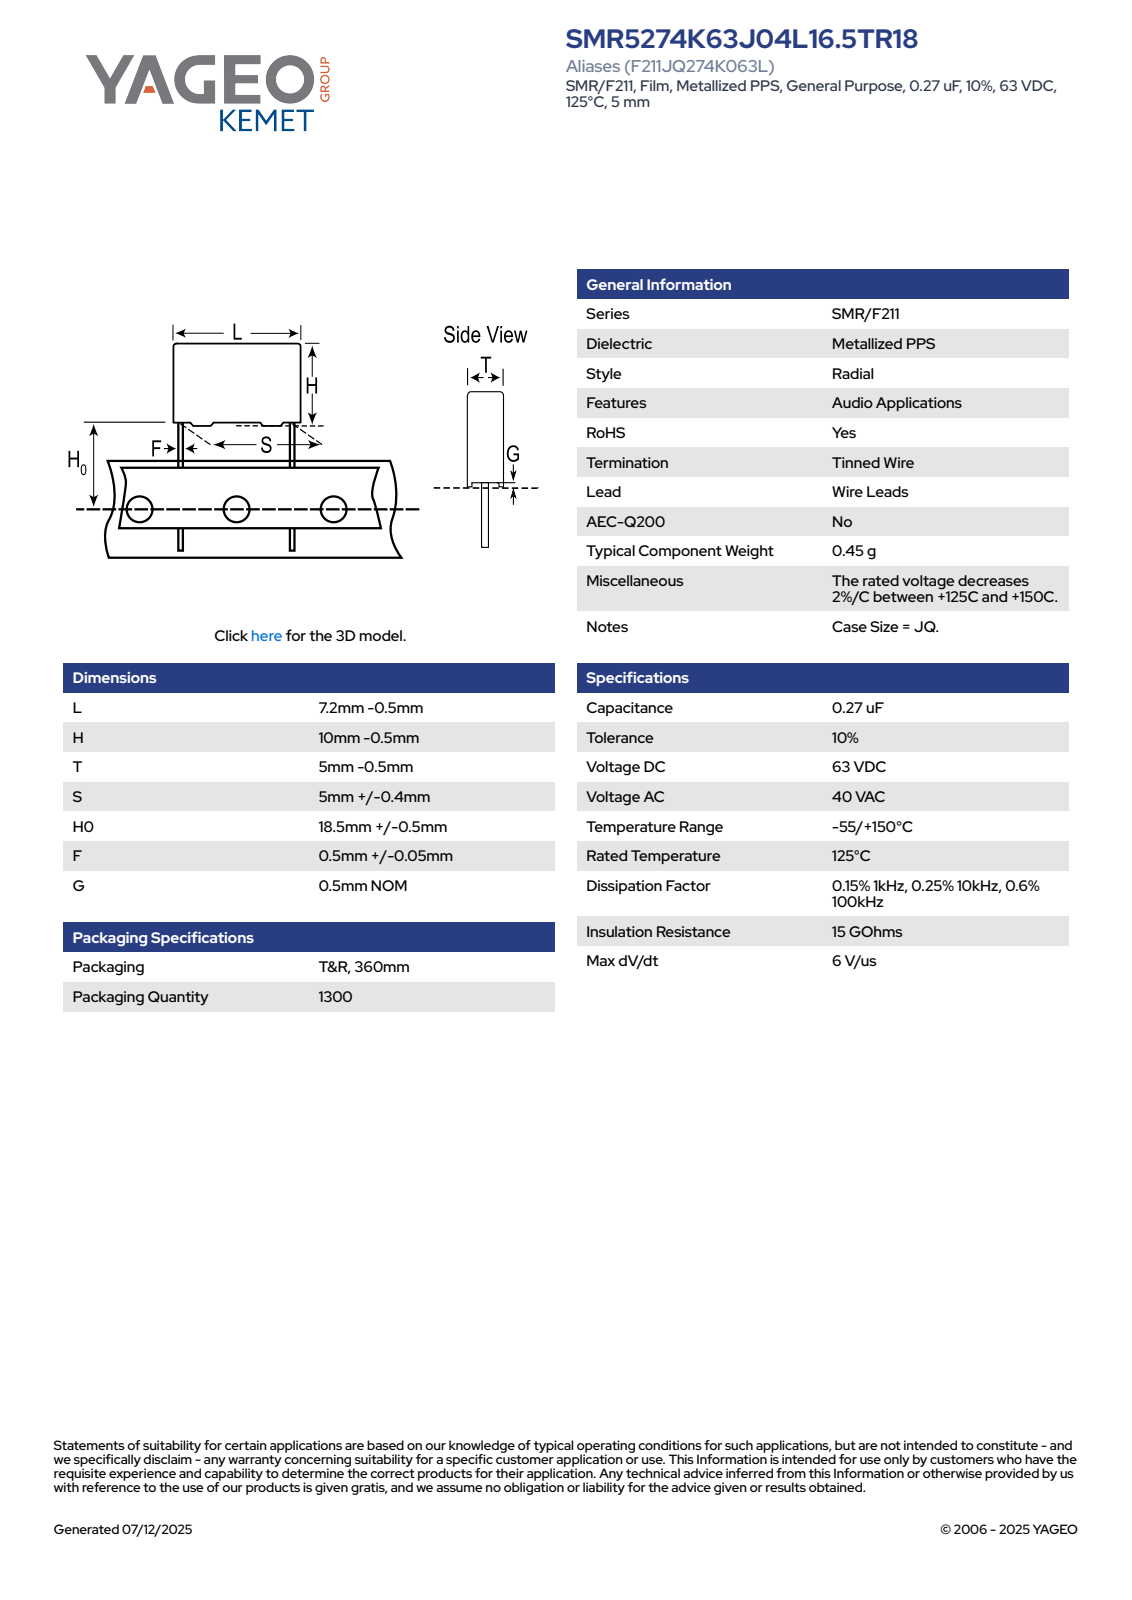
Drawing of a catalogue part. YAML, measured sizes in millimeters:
part_name: "CFR_RBG_7.2X10X5_L6.7H9.5T4.5S5H019F0.55G0.5"
step_written_by: "SolidWorks 2014 (AUTOMOTIVE_DESIGN)"
units: millimeters
bodies: {solids: 4, faces: 89, planar: 81, cylindrical: 8, other: 0}
overall_size: [28.5, 6.7, 4.5]
volume: 280
surface_area: 335
round_bosses_or_shafts:
  - {diameter: 0.55, count: 2}
partial_cylinders:
  - {radius: 0.5, count: 4}
face_to_face_distances: [4.5, 6.7, 9, 4.24, 3.98, 0.5, 9.5, 2.49, 19, 19.5]
